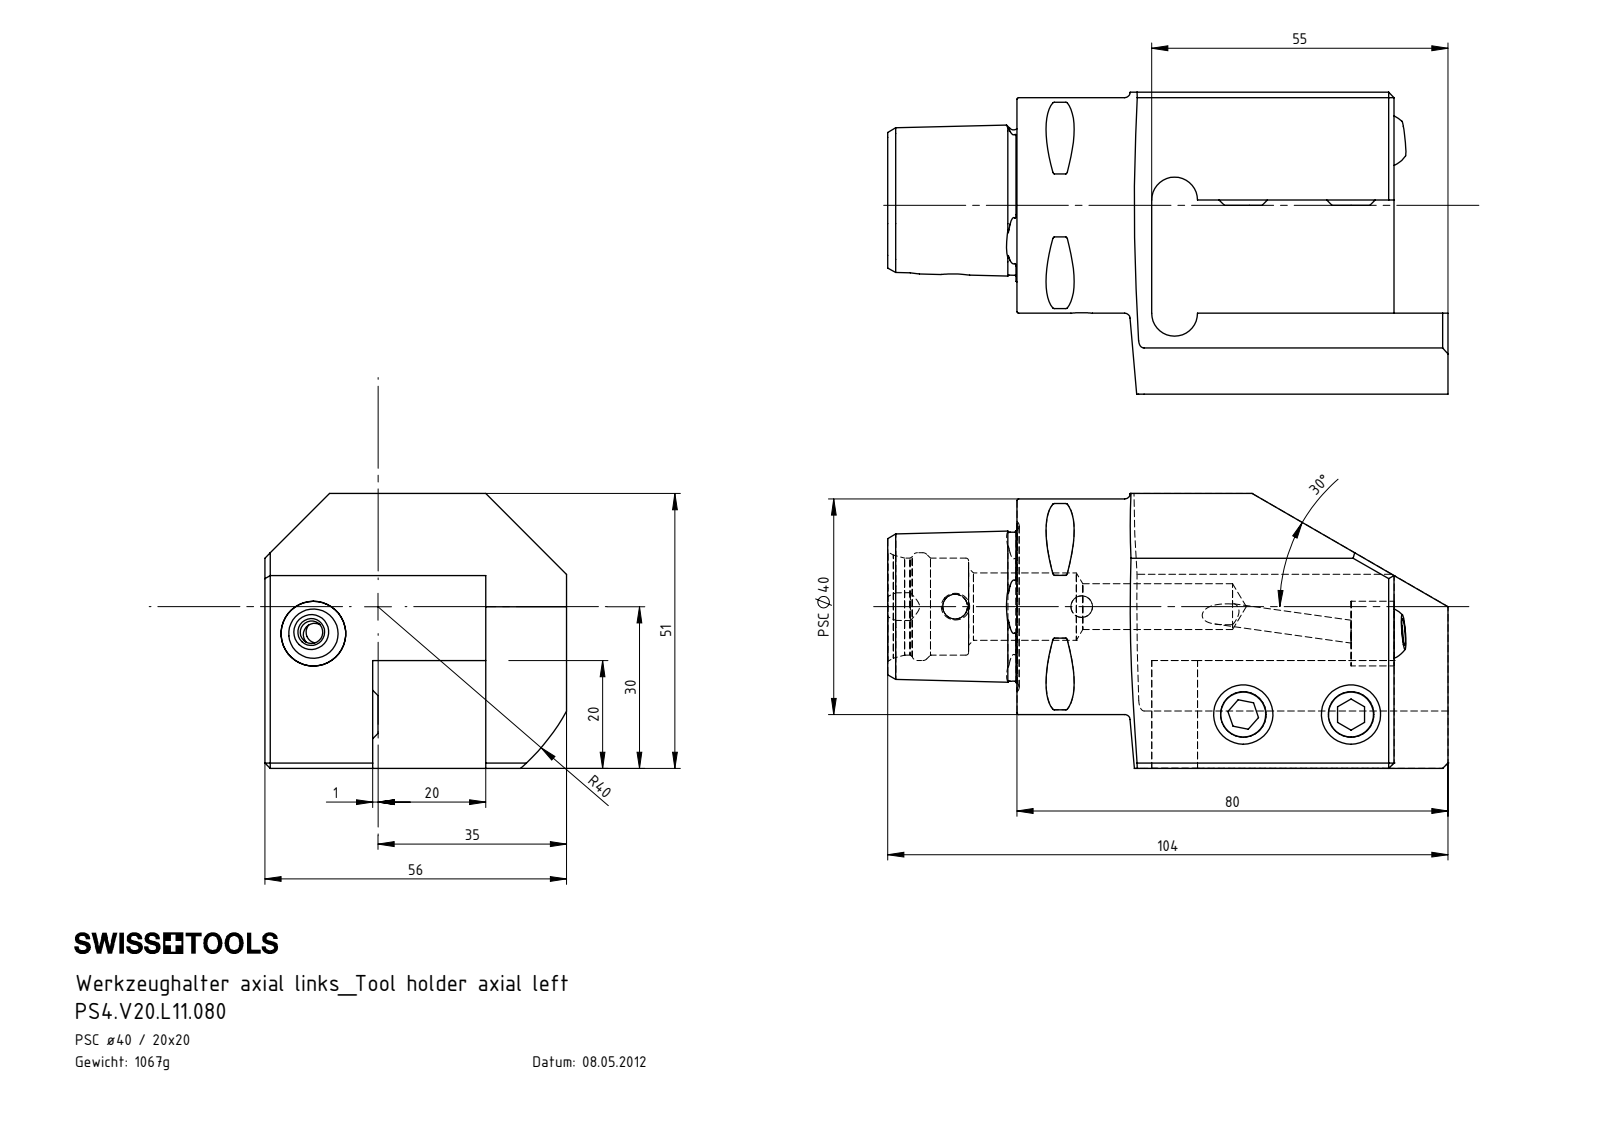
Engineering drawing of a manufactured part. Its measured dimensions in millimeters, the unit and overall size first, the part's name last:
Units: millimetres
Overall size (bounding box): 104 × 56 × 51
Round holes (diameter × count): ⌀8.5 ×3, ⌀4.2 ×2, ⌀4 ×1, ⌀4.6 ×1, ⌀7 ×1, ⌀12 ×1, ⌀12.5 ×1, ⌀18 ×1, ⌀20 ×1
Round bosses / shafts (diameter × count): ⌀10 ×2, ⌀40 ×1
Partial cylindrical surfaces — rounded edges, fillets, slot ends (radius × count): R0.3 ×8, R5 ×2, R3 ×1, R40 ×1
Main face-to-face distances: 20, 56, 15, 41, 21, 31, 51, 36, 55, 70
Hole centre spacings: 13, 20, 23.5, 36.06, 53.85, 57.12, 76.17
Volume: 135 810 mm³ · Surface area: 27 964 mm²
Bodies: 5 solids, 214 faces (59 planar, 48 cylindrical, 107 other)
Part name (STEP PRODUCT): KU1-U12.001.010_2; KU1-U12.001.010_1; PS4-V20.L11.080_A; ISO 4026 - M10 x 20 (+2 more)
STEP written by: SolidWorks 2017 (AUTOMOTIVE_DESIGN)
